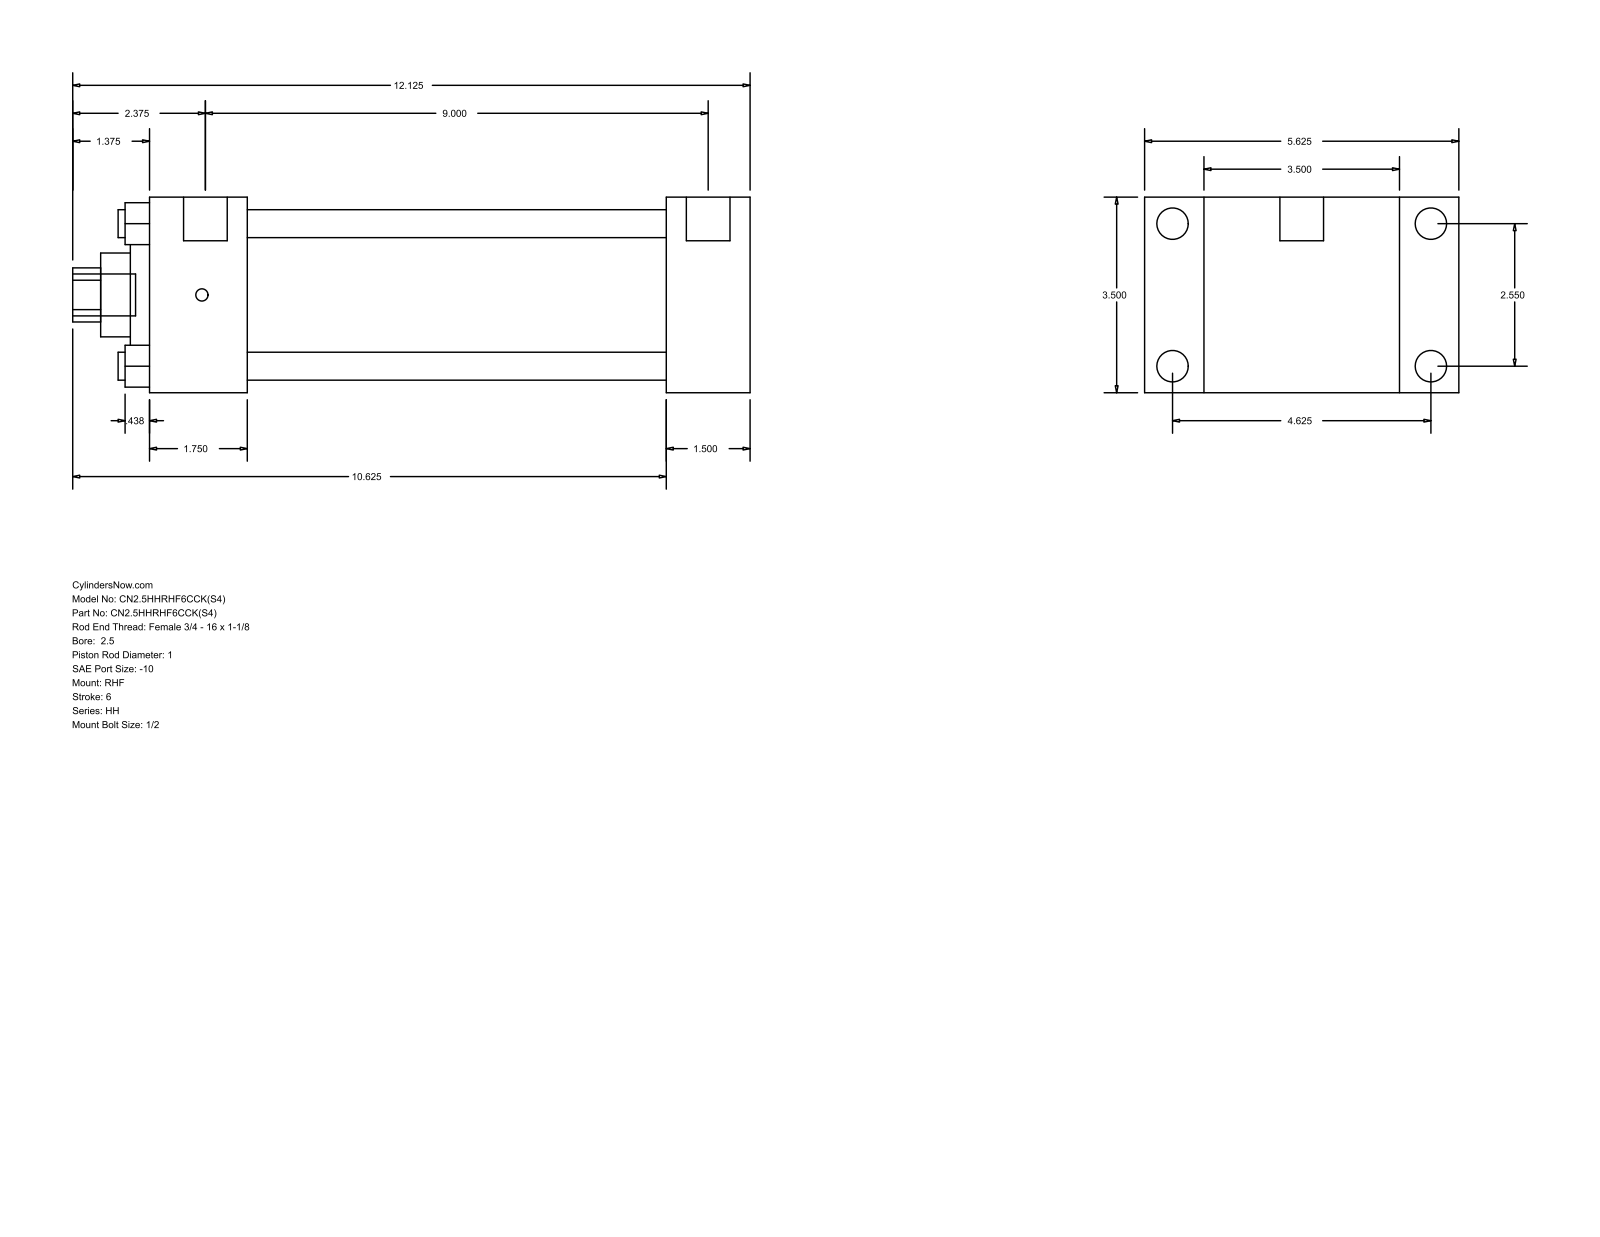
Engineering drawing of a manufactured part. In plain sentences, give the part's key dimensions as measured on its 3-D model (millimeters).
The part is named "HH_RHF__0250_1". Its 3-D file was written by "GSSL Pune (CONFIG_CONTROL_DESIGN)". It is 0 solids with 90 faces: 61 planar, 29 cylindrical and 0 other. Overall it measures 307.98 by 142.88 by 88.9 millimeters. Round holes: 4 of diameter 12.7, 1 of diameter 25.4, 1 of diameter 38.1, 1 of diameter 60.33, 1 of diameter 73.03. Round bosses or shafts: 4 of diameter 14.3, 4 of diameter 5.56, 2 of diameter 19.84, 1 of diameter 19.05. Partial cylindrical surfaces (rounded edges, fillets, slot ends): 1 of radius 12.29. The main face-to-face distances are 88.9, 38.1, 26.99, 115.89, 234.96, 273.06, 142.88, 44.46, 190.5, 228.6. The hole center spacings are 45.79, 64.76, 91.58.
